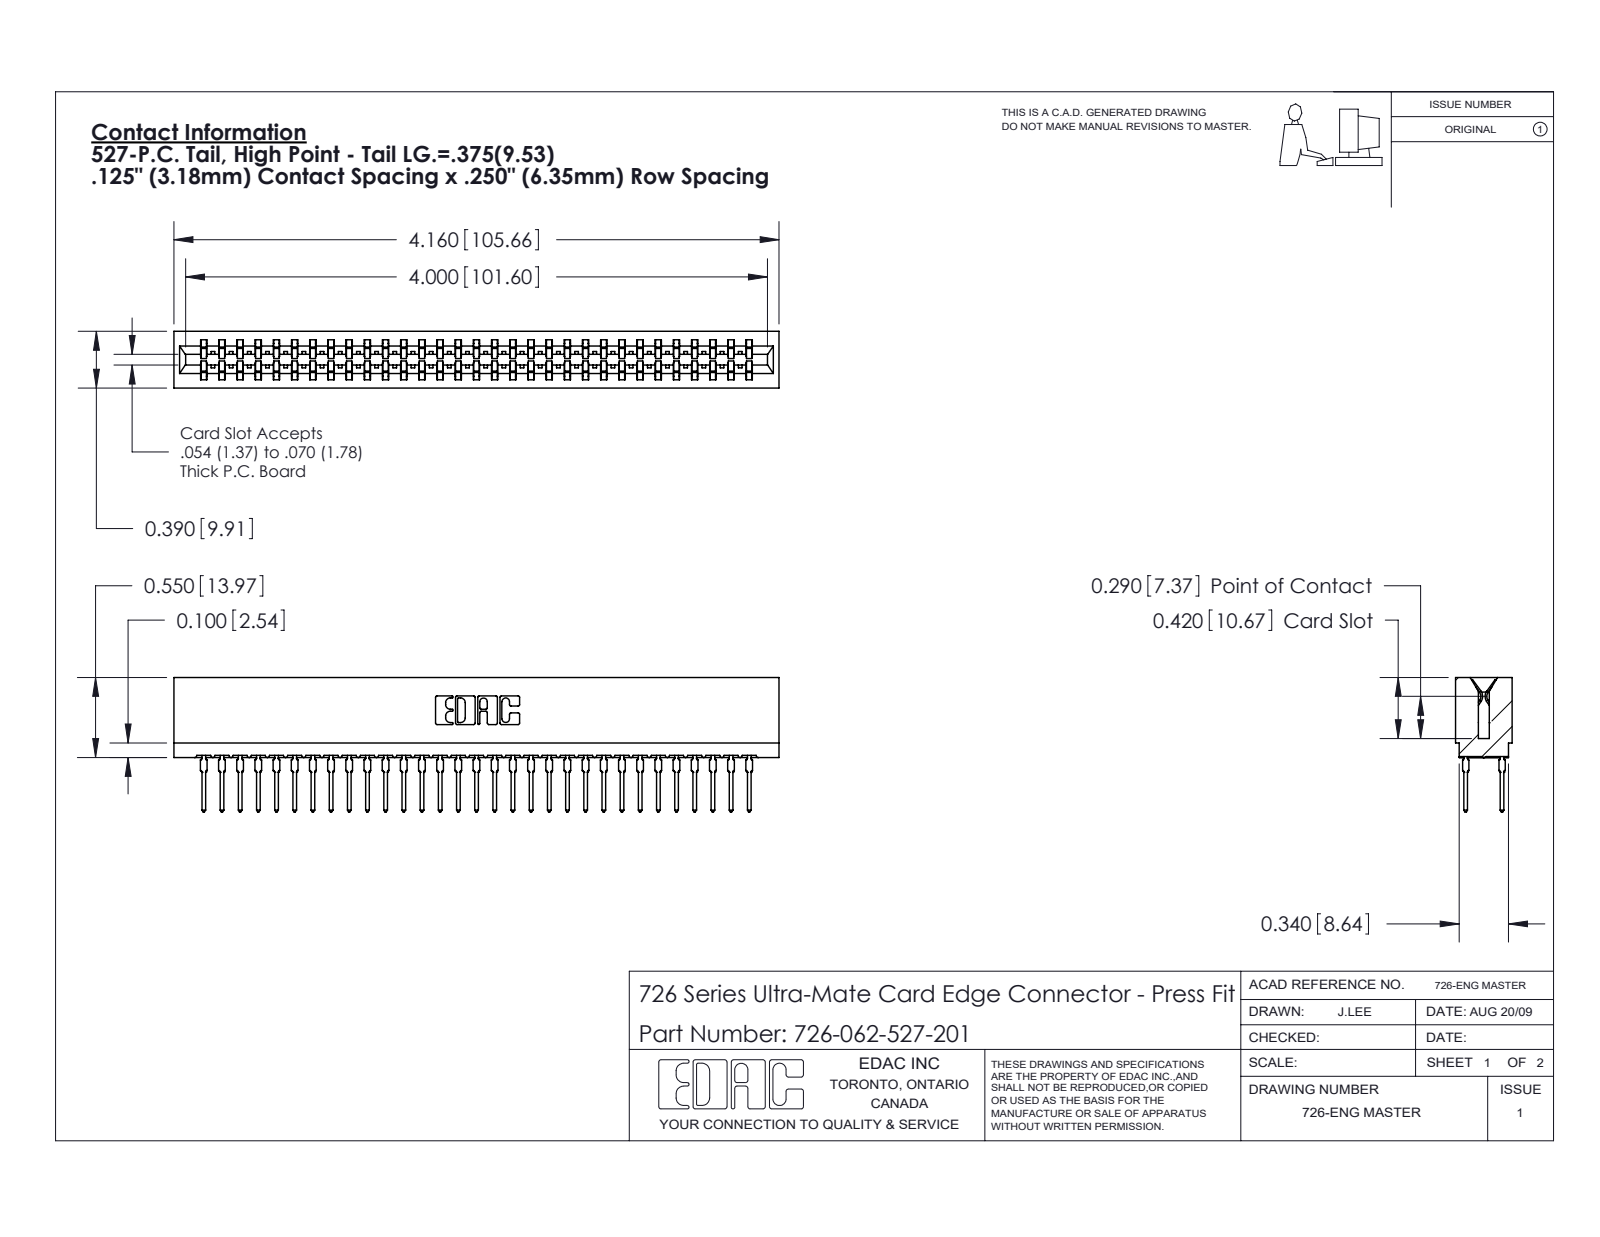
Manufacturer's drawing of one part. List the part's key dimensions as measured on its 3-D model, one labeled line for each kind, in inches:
Part name (STEP PRODUCT): 746-292-001_527; 726-062-527-201; 726 Part_.515 Slot Depth - 01
STEP written by: SolidWorks 2020 (CONFIG_CONTROL_DESIGN)
Units: inches
Bodies: 63 solids, 5646 faces (2907 planar, 1127 cylindrical, 1612 other)
Overall size (bounding box): 4.16 × 0.924 × 0.39
Volume: 0.603 in³ · Surface area: 25.99 in²
Partial cylindrical surfaces — rounded edges, fillets, slot ends (radius × count): R0.021 ×124, R0.015 ×32, R0.01 ×22, R0.005 ×8, R0.011 ×8, R0.007 ×6, R0.031 ×6, R0.026 ×3
Main face-to-face distances: 0.057, 0.333, 0.25, 0.025, 0.307, 0.39, 0.275, 0.083, 1, 0.365
